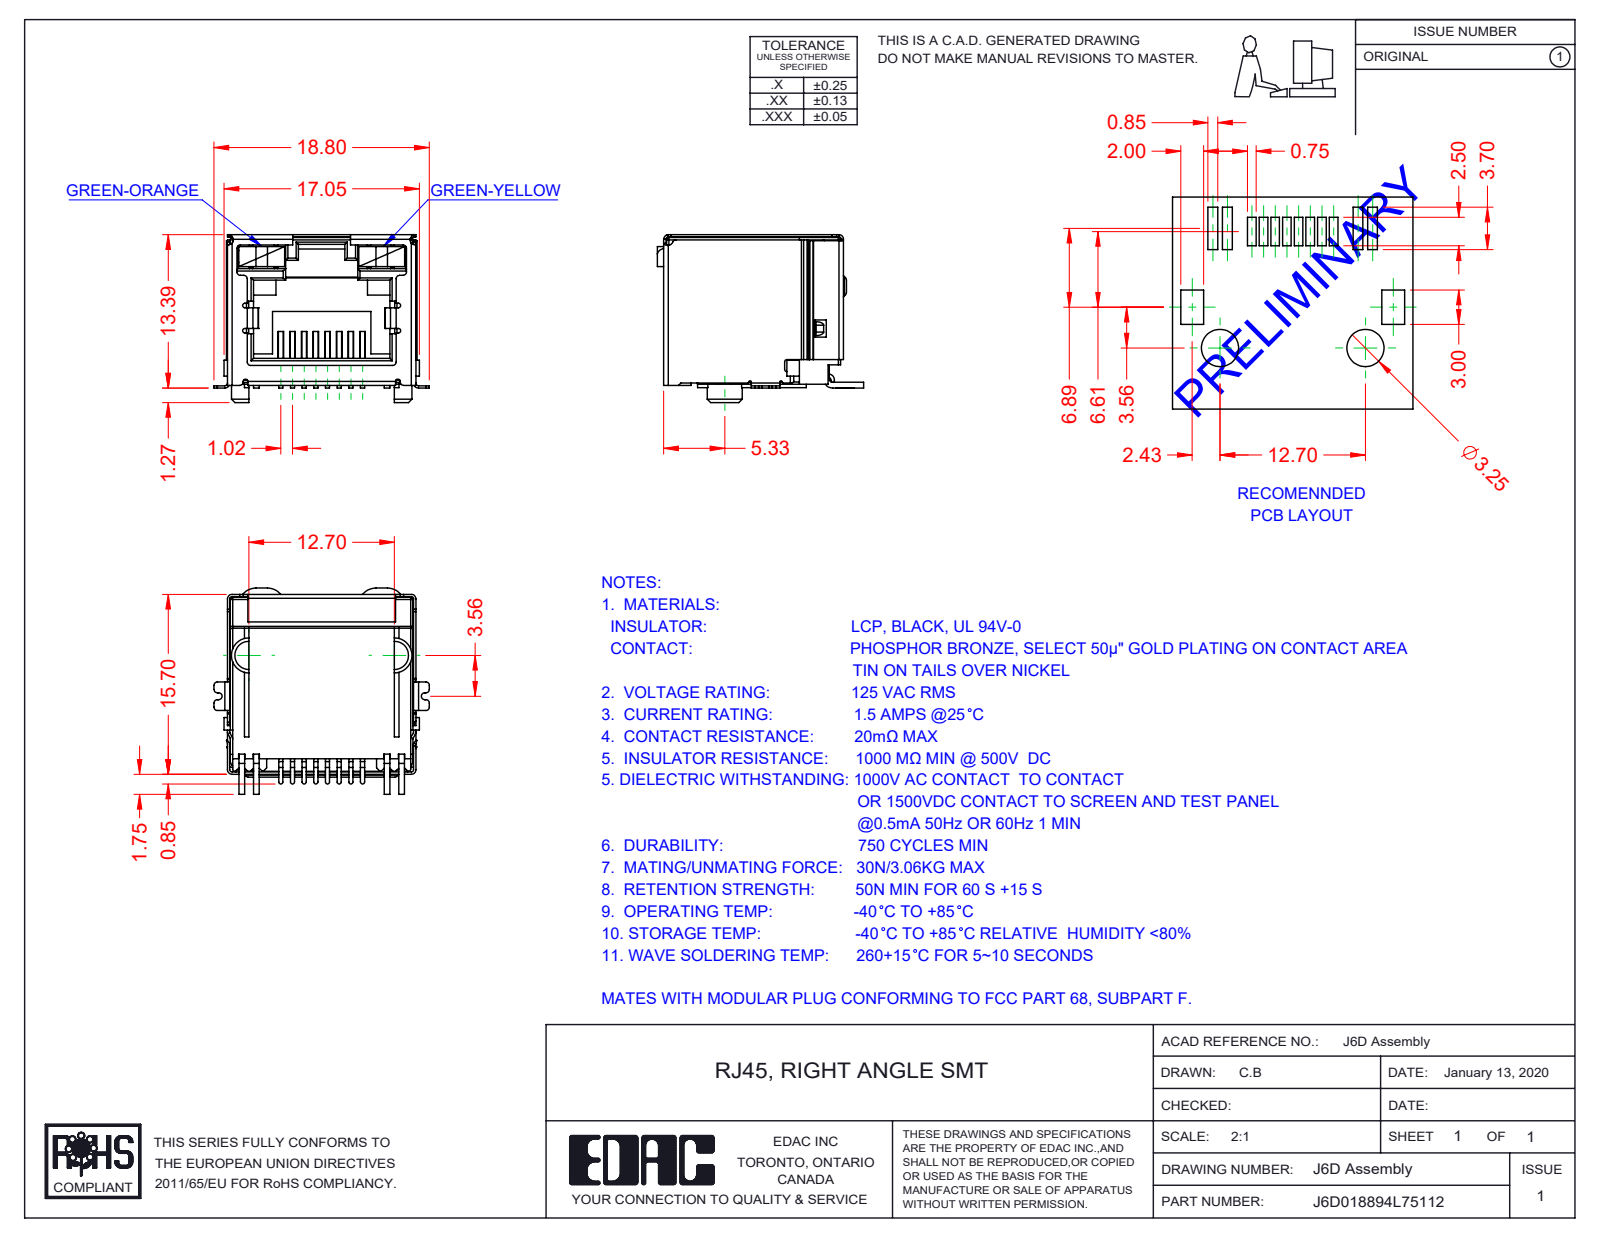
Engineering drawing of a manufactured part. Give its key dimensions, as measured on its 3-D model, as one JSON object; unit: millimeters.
{"part_name": "6D Contacts; 6D Insulator; J6D018894L75112; 6D Shield_LED - No EMI (+2 more)", "step_written_by": "SolidWorks 2016 (CONFIG_CONTROL_DESIGN)", "units": "millimeters", "bodies": {"solids": 12, "faces": 899, "planar": 646, "cylindrical": 220, "other": 33}, "overall_size": [18.8, 18, 14.65], "volume_mm3": 1804, "surface_area_mm2": 4898, "partial_cylinders_radius": [[0.3, 39], [0.2, 37], [0.4, 16], [0.1, 12], [0.15, 8], [0.18, 8], [0.5, 6], [1.5, 5]], "face_to_face_distances": [16, 16.25, 16.2, 2.25, 1, 15.95, 16.05, 12.8, 0.45, 16.45]}
